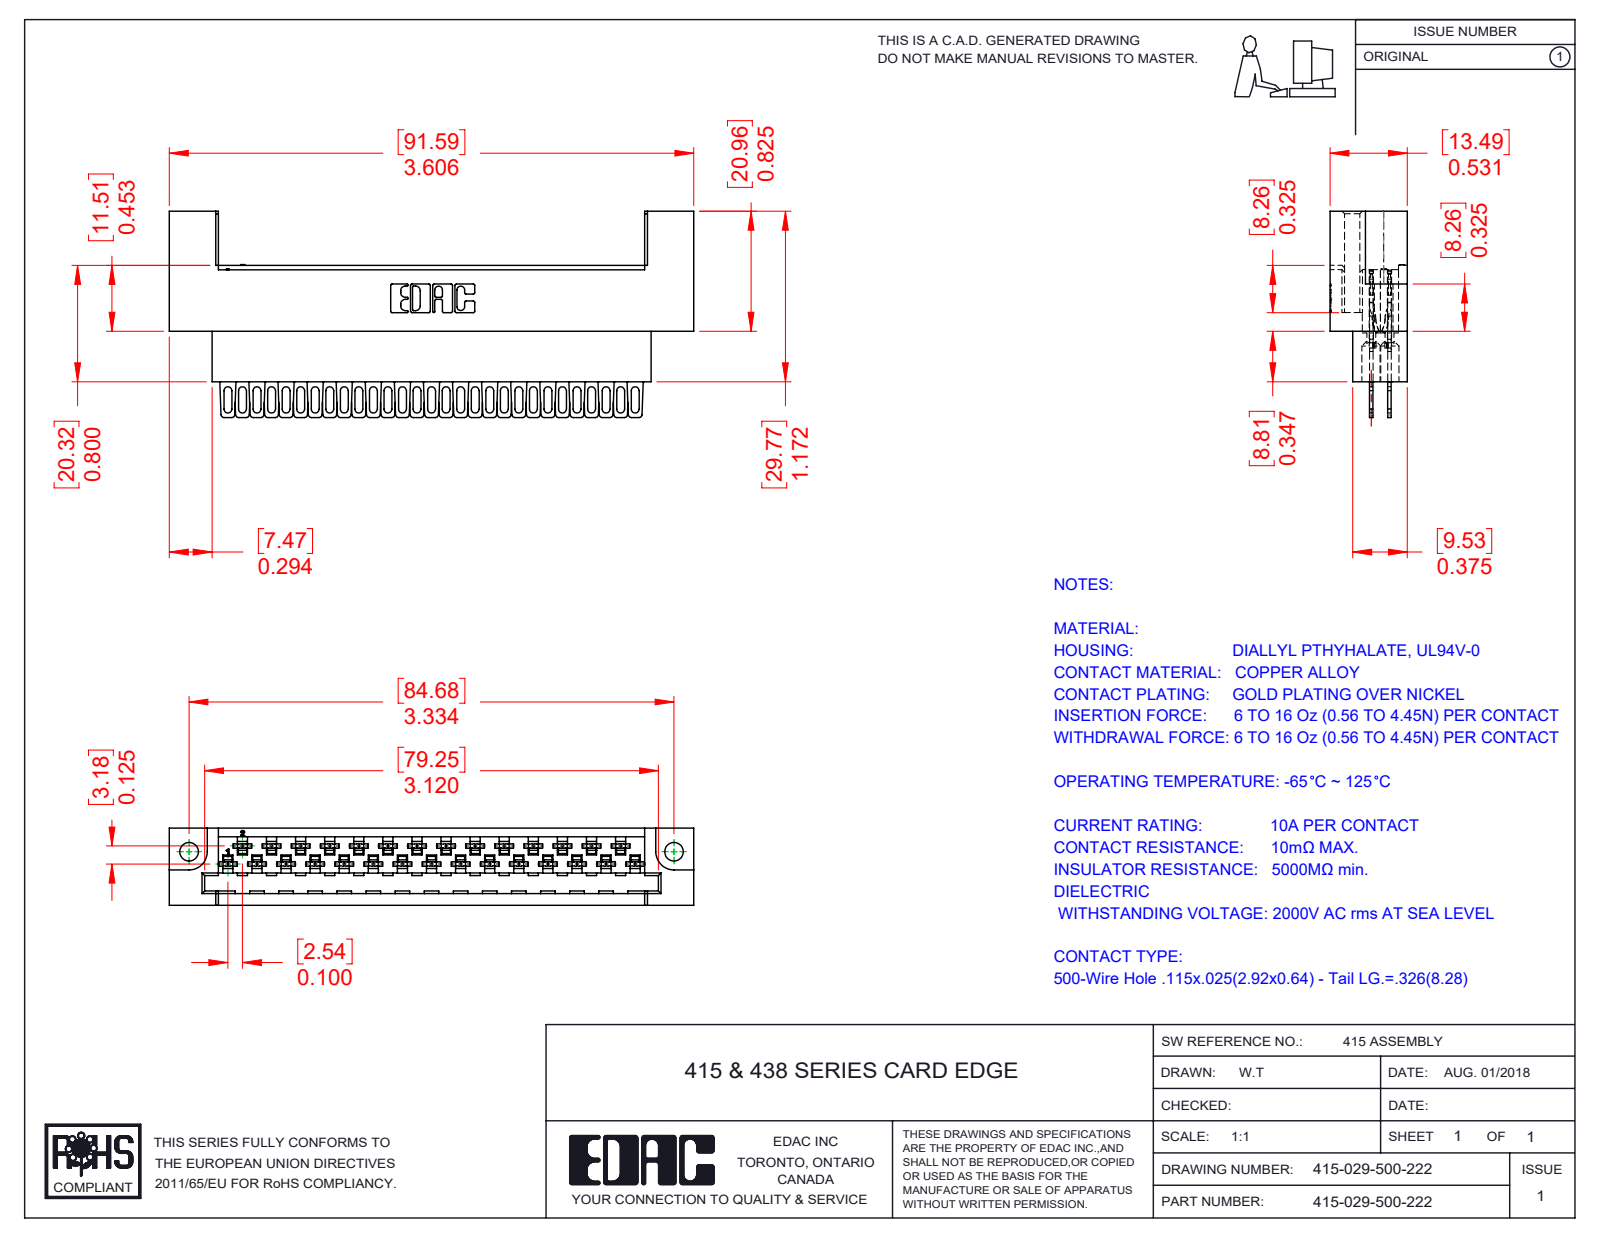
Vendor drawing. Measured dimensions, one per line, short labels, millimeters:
name: 415-029-500-222; 516-290-001_500; 415-210-001_415-210-029-222
written by: SolidWorks 2016 (CONFIG_CONTROL_DESIGN)
unit: mm
bodies: 30 solids, 3118 faces (1948 planar, 887 cylindrical, 283 other)
size: 91.59 × 36 × 13.49
volume: 15 912 mm³; area: 20 006 mm²
holes: 29× ⌀1.27, 29× ⌀3.3, 2× ⌀3.25
rounds: 116× R0.3, 116× R0.56, 58× R0.18, 58× R0.2, 58× R0.41, 58× R0.51, 58× R0.69, 58× R2.03
face distances: 3.18, 0.61, 13.49, 7.49, 1.27, 1.88, 6.61, 6.88, 6, 2.82
hole spacings: 5.08, 10.16, 15.24, 20.32, 25.4, 30.48, 35.56, 2.54
